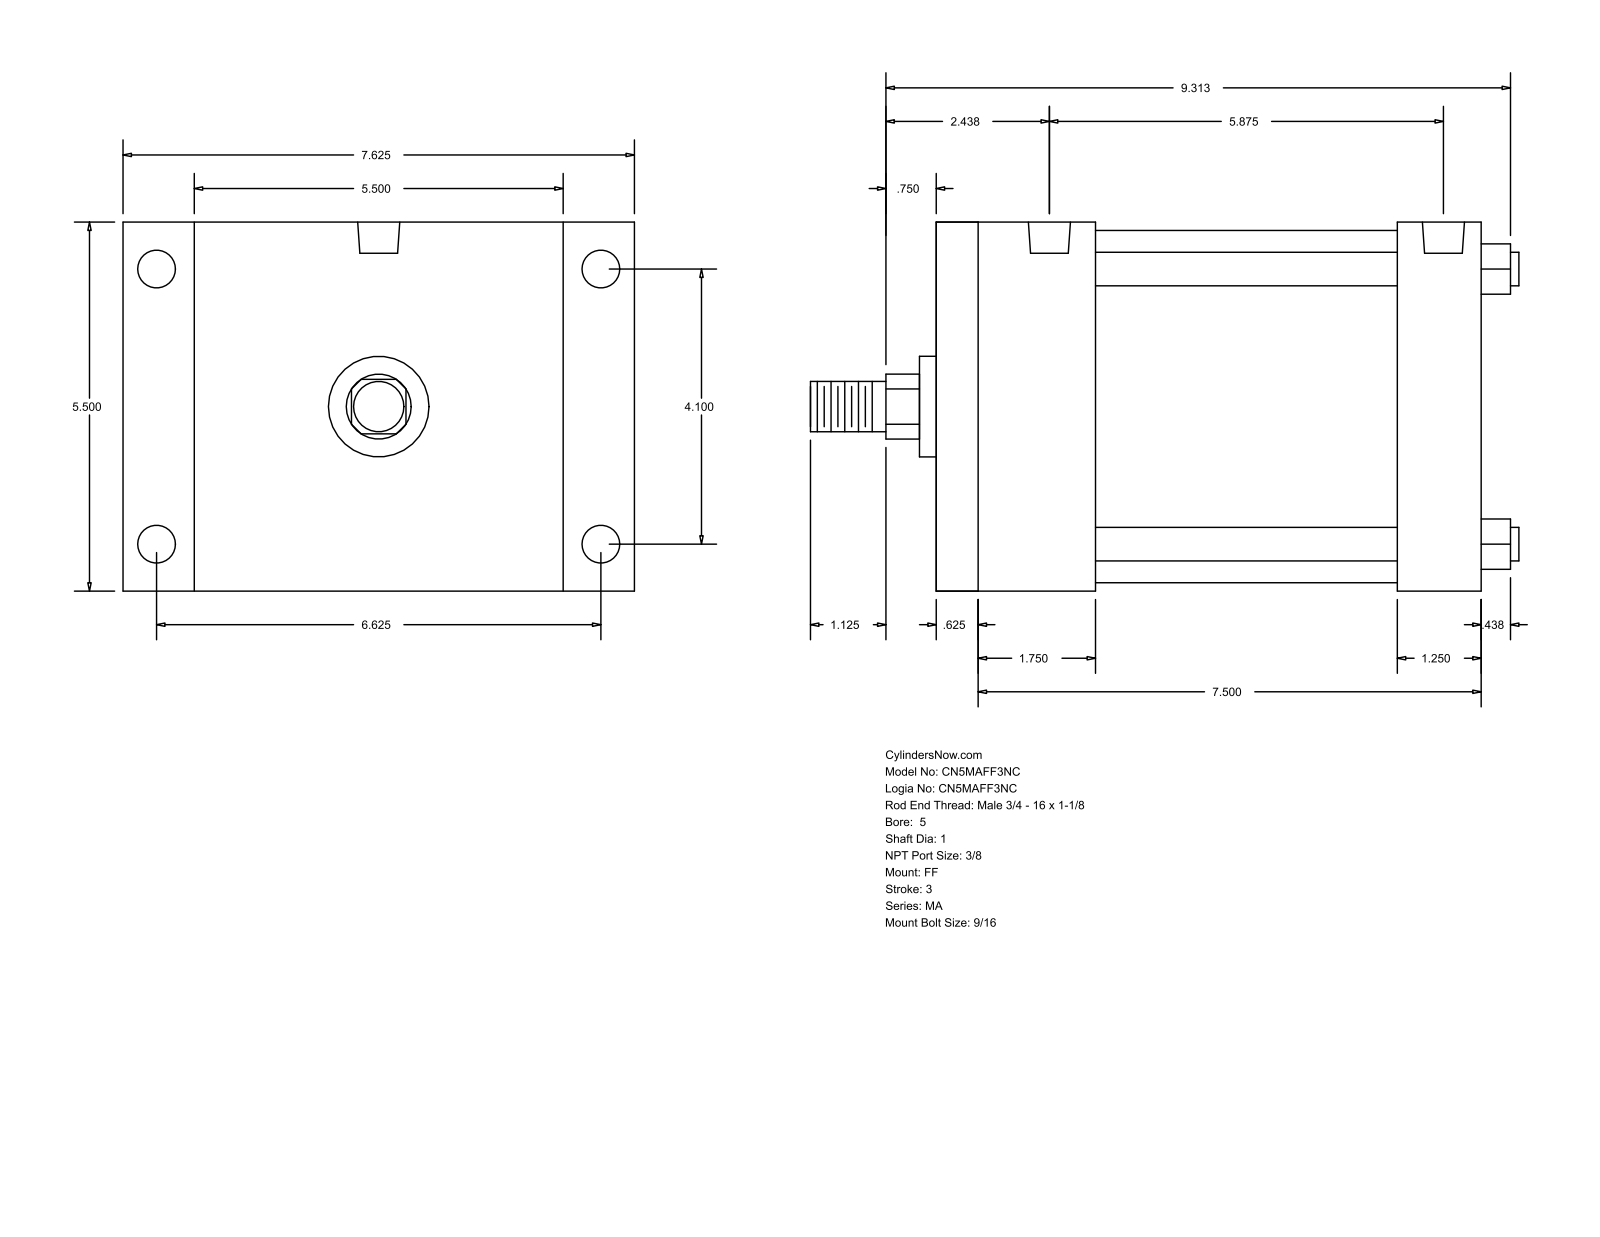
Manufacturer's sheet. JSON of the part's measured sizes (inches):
{"part_name": "MA_FF__0500_1", "step_written_by": "GSSL Pune (CONFIG_CONTROL_DESIGN)", "units": "inches", "bodies": {"solids": 0, "faces": 92, "planar": 64, "cylindrical": 28, "other": 0}, "overall_size": [10.563, 7.625, 5.5], "round_holes": [[0.437, 4], [0.563, 4], [0.627, 2]], "round_bosses_or_shafts": [[0.5, 4], [5.25, 1], [1.5, 1], [1, 1], [0.75, 1]], "partial_cylinders_radius": [[0.484, 1]], "face_to_face_distances": [5.5, 8.125, 0.625, 7.5, 6.875, 6.25, 1.25, 2.375, 1.75, 4.5], "hole_center_spacings": [0.187, 4.1, 5.5, 5.688, 6.625, 7.791, 5.875]}
